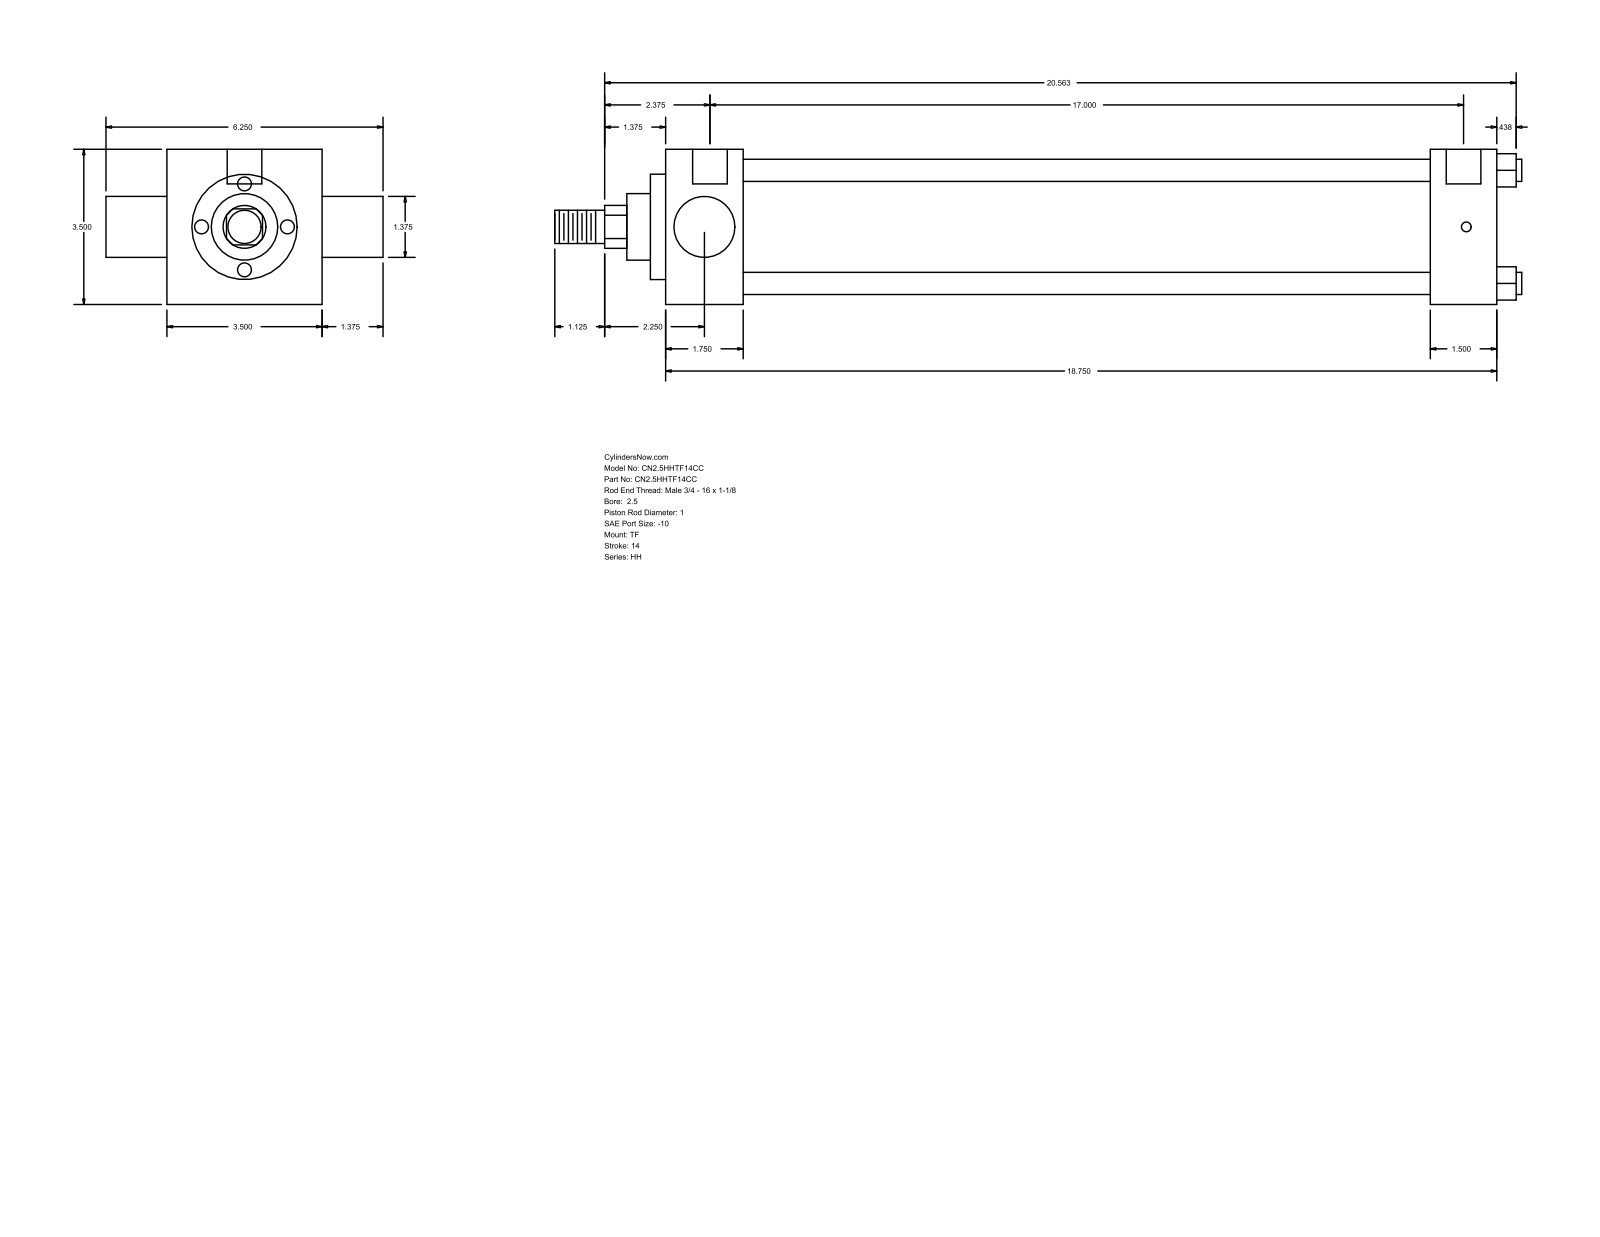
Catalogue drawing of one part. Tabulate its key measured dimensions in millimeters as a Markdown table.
| quantity | value |
| --- | --- |
| part name | HH_TF__0250_1 |
| STEP written by | GSSL Pune (CONFIG_CONTROL_DESIGN) |
| units | millimeters |
| bodies | 0 solids, 86 faces (61 planar, 25 cylindrical, 0 other) |
| overall size | 554.04 × 158.75 × 88.9 |
| round holes (diameter × count) | 5.56 × 3, 19.84 × 2 |
| round bosses / shafts (diameter × count) | 12.7 × 4, 73.03 × 1, 60.33 × 1, 38.1 × 1, 34.92 × 1, 25.4 × 1, 19.05 × 1 |
| partial cylindrical surfaces (radius × count) | 12.29 × 1 |
| main face-to-face distances | 88.9, 476.26, 44.46, 431.8, 438.15, 393.69, 38.11, 34.93, 123.83, 8.73 |
| hole center spacings | 1.59, 433.38, 431.79, 434.97 |
